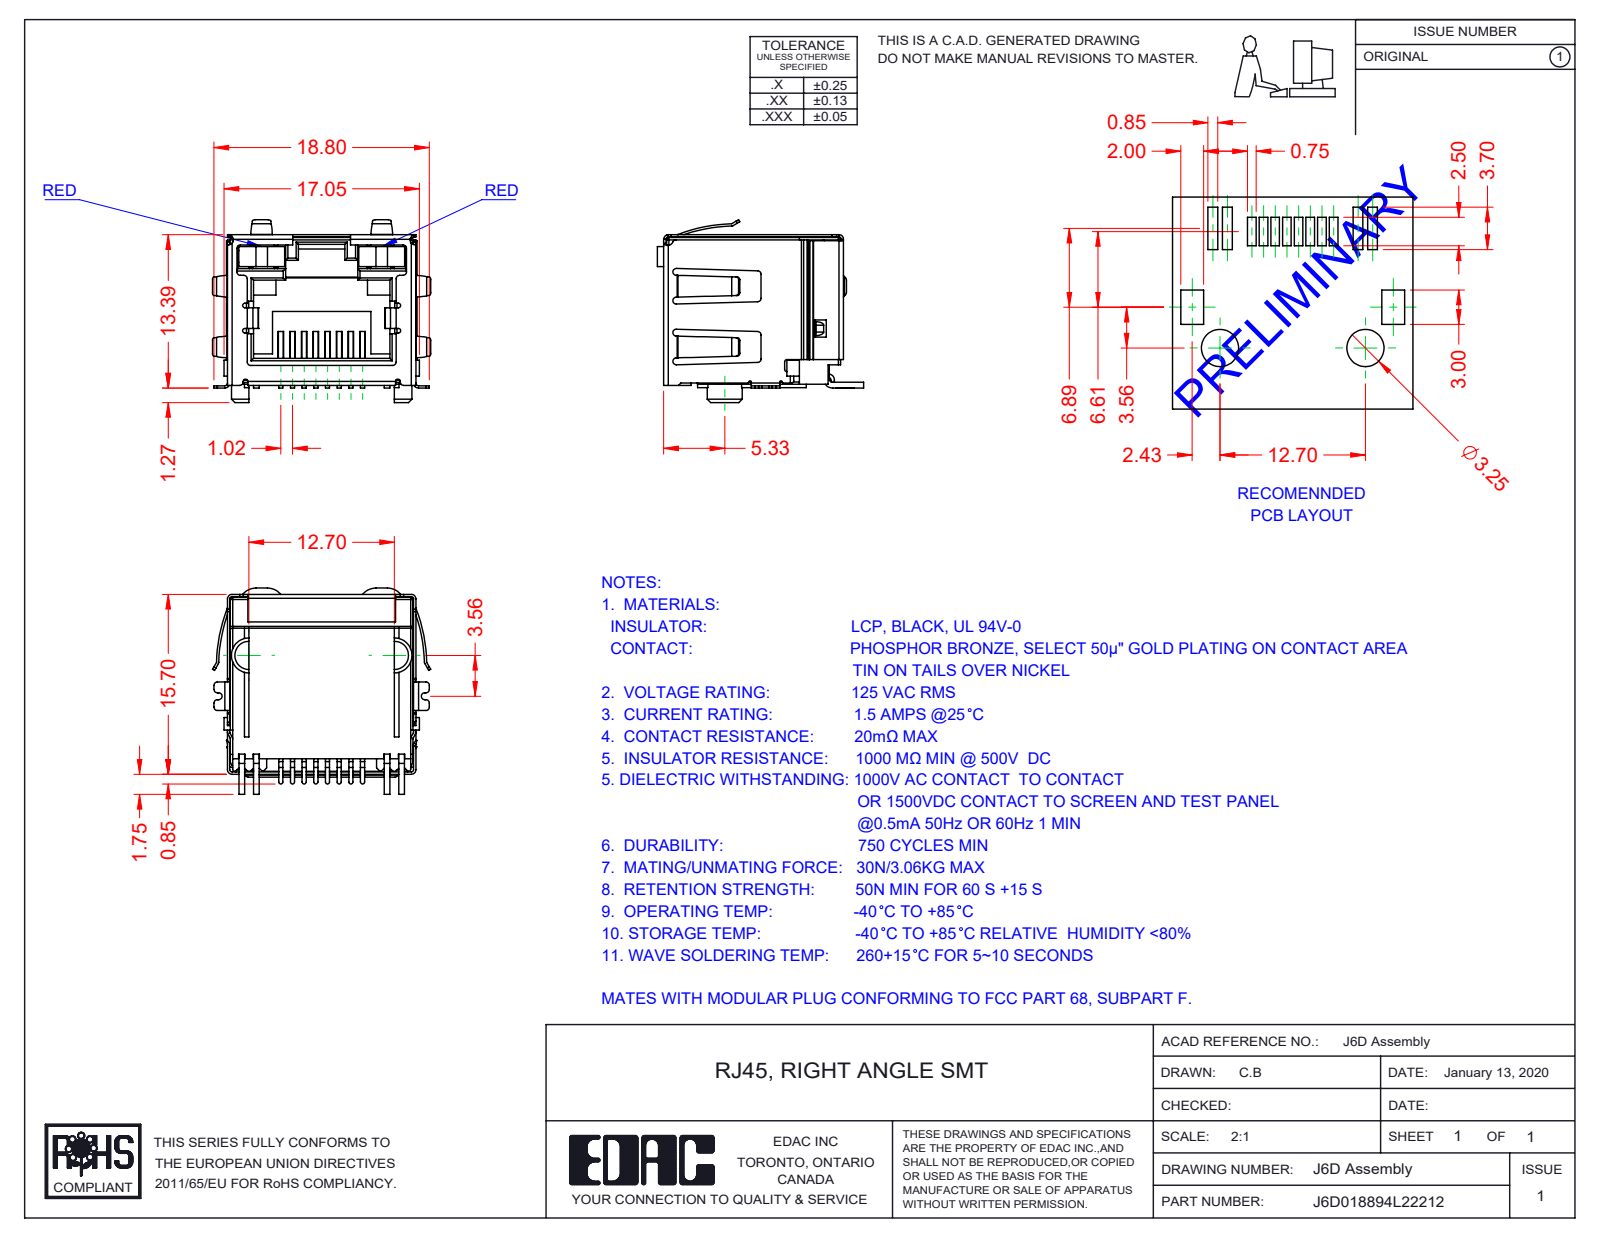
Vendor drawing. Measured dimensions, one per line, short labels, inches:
name: 6D Contacts; 6D Insulator; 6D LED RH_2-Red; 6D Shield_LED - EMI (+2 more)
written by: SolidWorks 2016 (CONFIG_CONTROL_DESIGN)
unit: in
bodies: 12 solids, 1028 faces (701 planar, 282 cylindrical, 45 other)
size: 0.75 × 0.709 × 0.628
volume: 0.109 in³; area: 7.434 in²
rounds: 55× R0.012, 40× R0.008, 19× R0.016, 16× R0.01, 12× R0.004, 8× R0.006, 8× R0.007, 6× R0.02
face distances: 0.63, 0.638, 0.64, 0.089, 0.039, 0.628, 0.504, 0.018, 0.514, 0.417
